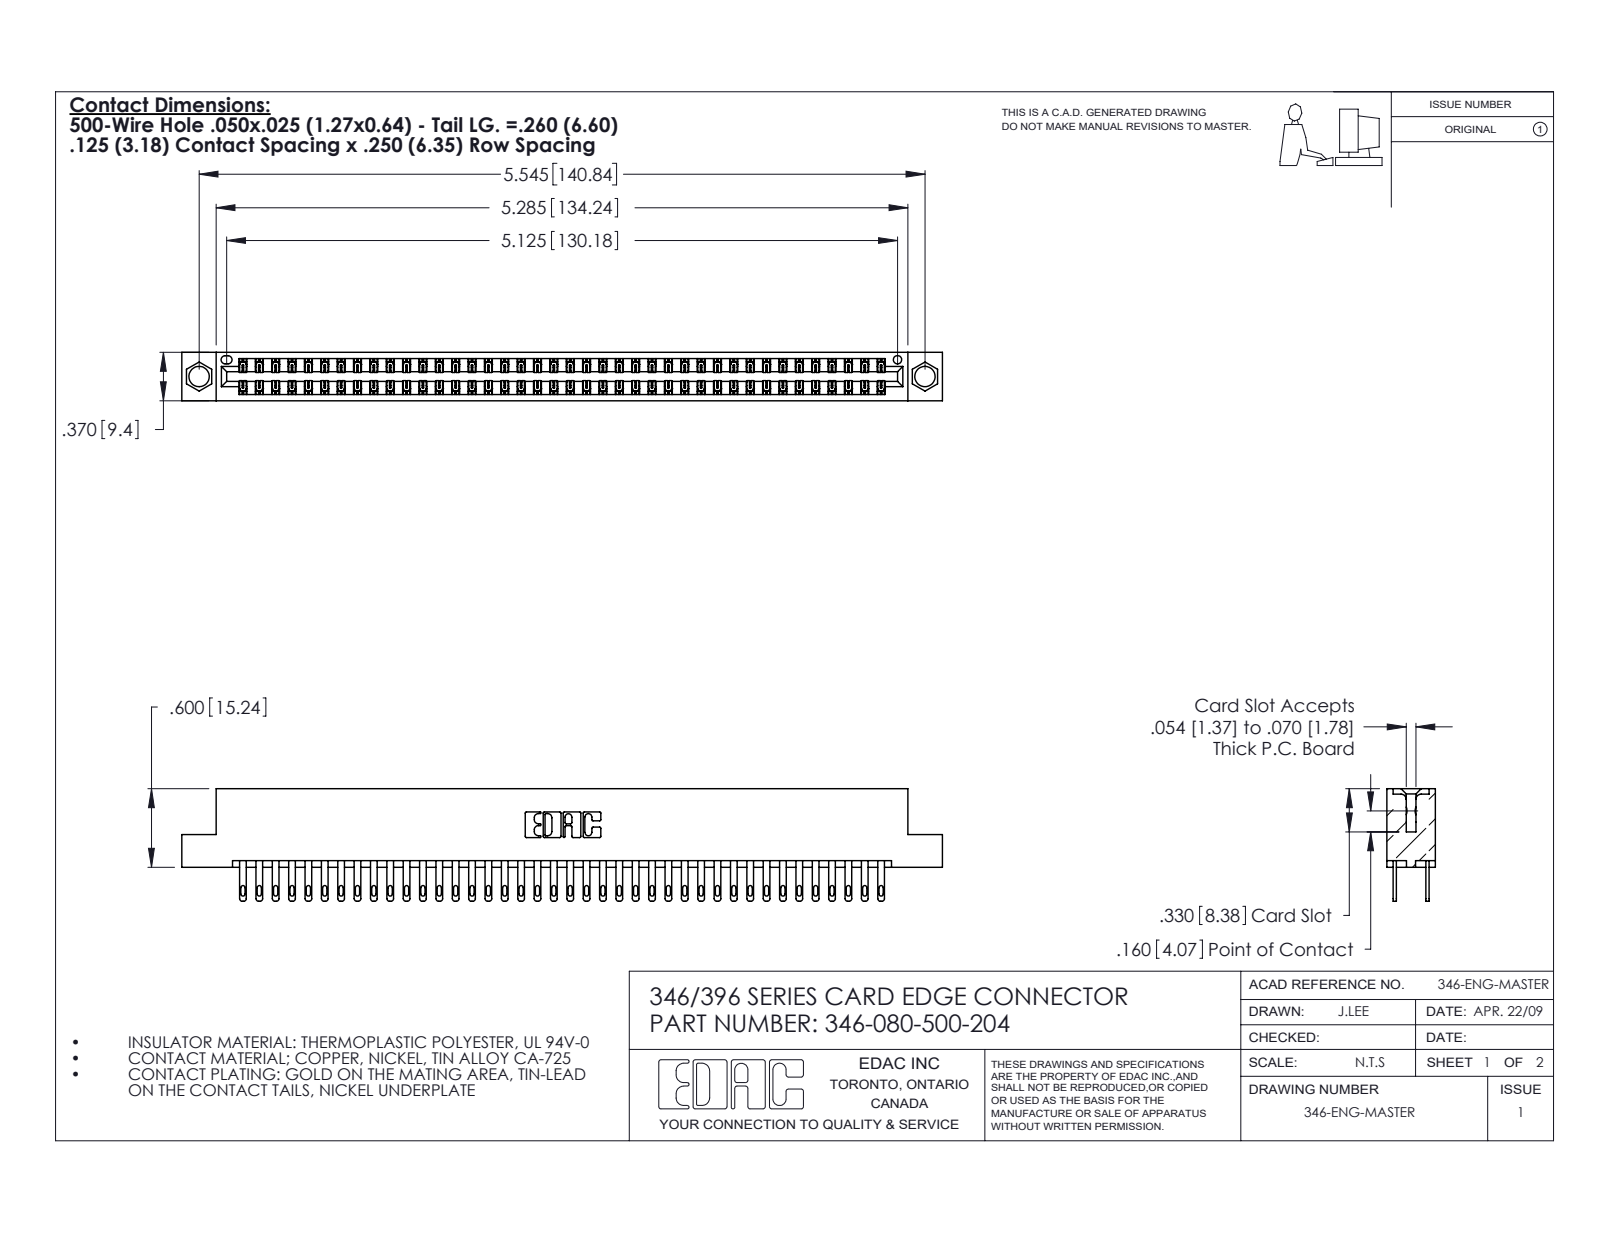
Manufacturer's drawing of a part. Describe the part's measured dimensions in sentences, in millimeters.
The part is named "346 Part_Flush Mounting Lugs - 0.156 Dia-TH; 346-080-500-204; 345-292-001_345-293-100". Its 3-D file was written by "SolidWorks 2020 (CONFIG_CONTROL_DESIGN)". It is 81 solids with 3976 faces: 2410 planar, 1566 cylindrical and 0 other. Overall it measures 147.6 by 21.8 by 9.4 millimeters. Its volume is 14 500 cubic millimeters and its surface area 20 610 square millimeters. Round holes: 2 of diameter 4, 1 of diameter 1.6. Partial cylindrical surfaces (rounded edges, fillets, slot ends): 120 of radius 0.2, 80 of radius 0.4, 80 of radius 0.5, 22 of radius 0.3, 6 of radius 0.2, 6 of radius 0.8, 3 of radius 0.7, 2 of radius 0.4. The main face-to-face distances are 1.2, 8.2, 6.4, 1.8, 7.6, 0.6, 9.4, 7, 3.8, 5.6. The hole center spacings are 6.2, 135.5, 140.8.
